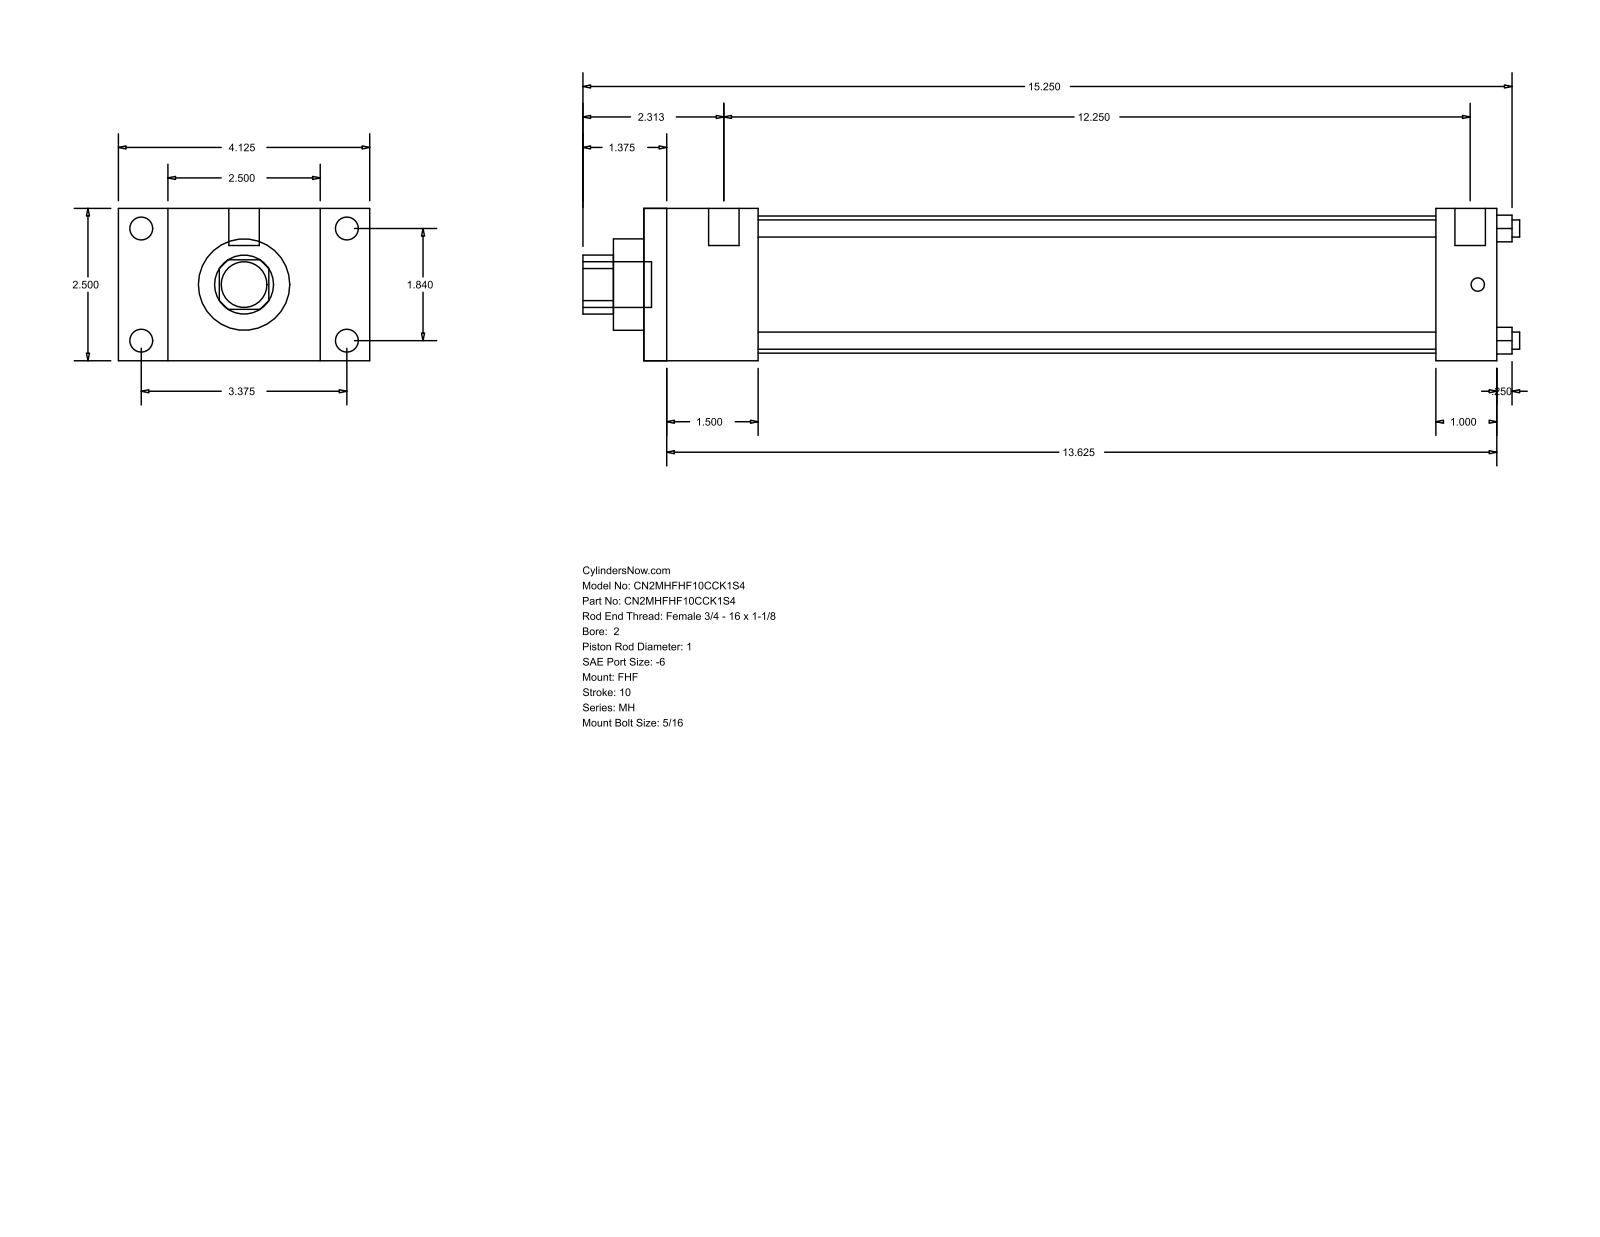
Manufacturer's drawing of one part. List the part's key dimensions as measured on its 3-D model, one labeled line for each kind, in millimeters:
Part name (STEP PRODUCT): MH_FHF__0200_1
STEP written by: GSSL Pune (CONFIG_CONTROL_DESIGN)
Units: millimetres
Bodies: 0 solids, 88 faces (60 planar, 28 cylindrical, 0 other)
Overall size (bounding box): 390.52 × 104.78 × 63.5
Round holes (diameter × count): ⌀7.14 ×4, ⌀25.4 ×1, ⌀38.1 ×1, ⌀57.15 ×1
Round bosses / shafts (diameter × count): ⌀9.53 ×4, ⌀5.56 ×4, ⌀12.7 ×2, ⌀19.05 ×1
Partial cylindrical surfaces — rounded edges, fillets, slot ends (radius × count): R12.29 ×1
Main face-to-face distances: 63.5, 355.6, 47.63, 307.97, 20.64, 84.14, 104.78, 25.4, 330.2, 282.57
Hole centre spacings: 33.05, 46.74, 66.1
